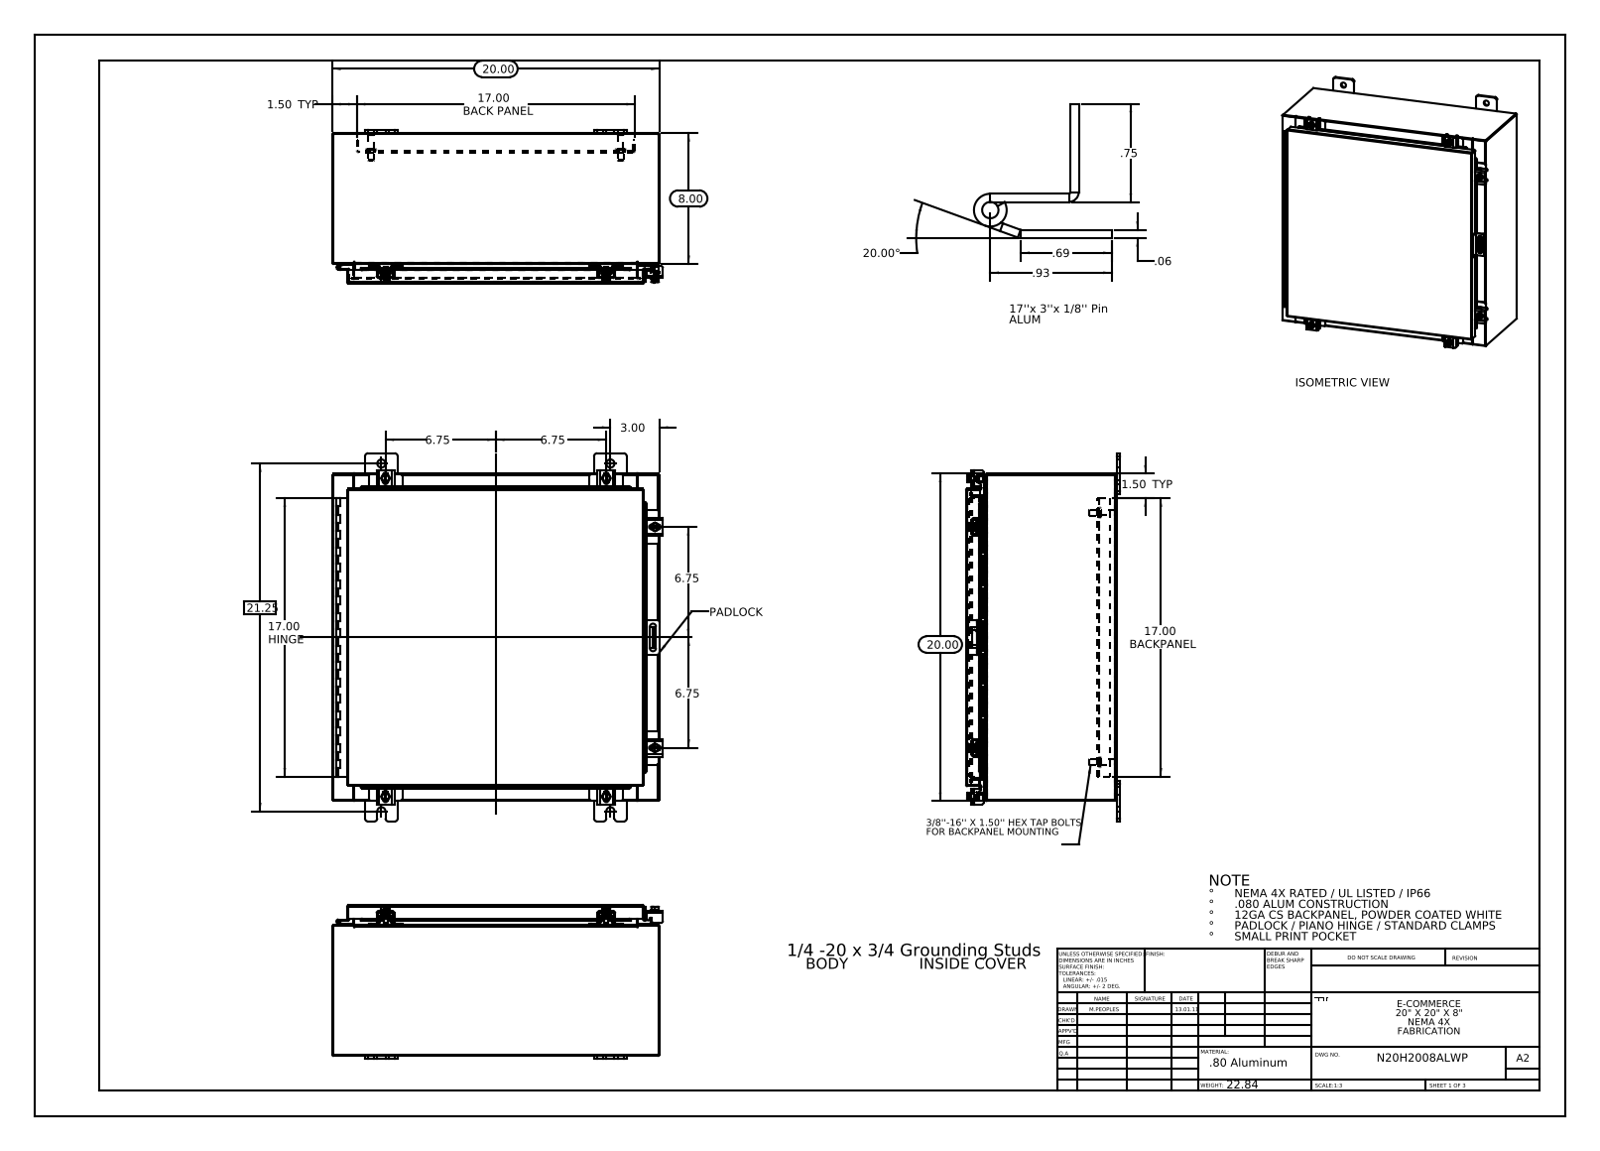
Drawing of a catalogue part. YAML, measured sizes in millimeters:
part_name: "N20H2008ALWP Top; N20H2008ALWP Padlock Hasp; N20H2008ALWP 125 Pin Hinge; N20H2008ALWP Hinge Cover Side (+8 more)"
step_written_by: "SolidWorks 2013 (CONFIG_CONTROL_DESIGN)"
units: millimeters
bodies: {solids: 47, faces: 1613, planar: 860, cylindrical: 657, other: 96}
overall_size: [571.5, 513.4, 238.5]
volume: 2633000
surface_area: 2618000
round_holes:
  - {diameter: 12.7, count: 8}
  - {diameter: 5.4, count: 6}
  - {diameter: 6.6, count: 6}
  - {diameter: 3.2, count: 2}
  - {diameter: 3.2, count: 1}
round_bosses_or_shafts:
  - {diameter: 6.4, count: 7}
  - {diameter: 12.7, count: 6}
  - {diameter: 10.1, count: 6}
  - {diameter: 15.9, count: 4}
  - {diameter: 9.5, count: 4}
  - {diameter: 8.4, count: 4}
partial_cylinders:
  - {radius: 1.5, count: 30}
  - {radius: 0.3, count: 25}
  - {radius: 4.8, count: 24}
  - {radius: 2.2, count: 21}
  - {radius: 3, count: 12}
  - {radius: 3.6, count: 12}
  - {radius: 3.2, count: 10}
  - {radius: 1.3, count: 9}
face_to_face_distances: [1.9, 231.8, 506.1, 233.7, 229.9, 504.2, 508, 2.6, 25.4, 27.3]
hole_center_spacings: [441.3, 369, 425.2, 572.3, 342.9, 10.9, 23.7, 47.2]
